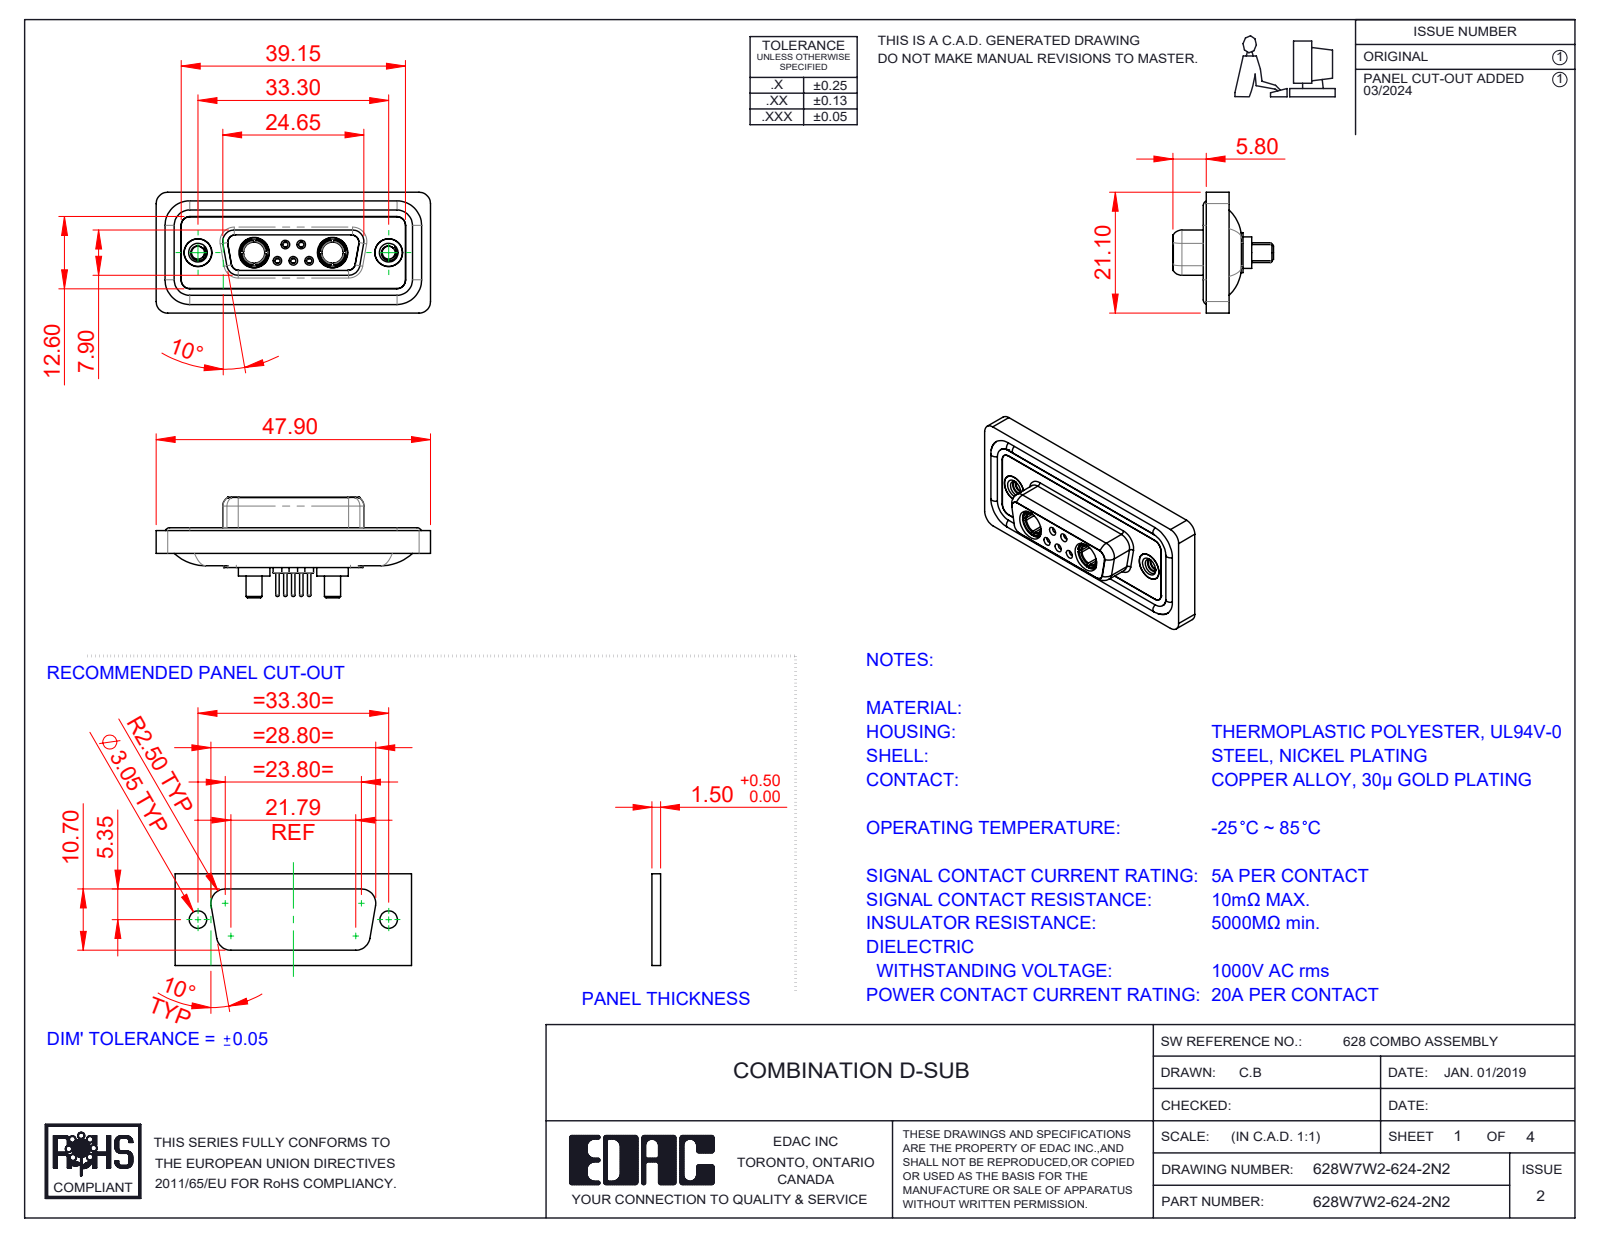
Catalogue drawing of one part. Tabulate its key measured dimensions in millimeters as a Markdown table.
| quantity | value |
| --- | --- |
| part name | 628Combo Housing_7W2; 628W7W2-624-2N2; Power Socket_20A S; 628Combo Shell Front_15 Contacts (+5 more) |
| STEP written by | SolidWorks 2023 (CONFIG_CONTROL_DESIGN) |
| units | millimeters |
| bodies | 16 solids, 809 faces (238 planar, 329 cylindrical, 242 other) |
| overall size | 47.9 × 21.1 × 17.55 |
| volume | 6 077 mm³ |
| surface area | 9 885 mm² |
| round holes (diameter × count) | 0.9 × 5, 1.1 × 5, 1.5 × 5, 2 × 5, 4.85 × 4, 1.6 × 3, 1.7 × 2, 2.26 × 2, 3.7 × 2, 4 × 2, 4.05 × 2, 5 × 2 |
| round bosses / shafts (diameter × count) | 1.6 × 6, 2.2 × 5, 0.6 × 5, 5.5 × 2, 5.2 × 2, 4.96 × 2, 4.95 × 2, 4.8 × 2 |
| partial cylindrical surfaces (radius × count) | 1.5 × 22, 2 × 20, 1.35 × 12, 1.6 × 8, 0.25 × 4, 0.5 × 4, 0.6 × 4, 0.65 × 4 |
| main face-to-face distances | 0.4, 1.8, 1.6, 0.5, 2.9, 7.45, 1.1, 5.65, 6.6, 7.05 |
| hole center spacings | 3.16, 2.77, 9.8, 23.5, 4.31, 4.33, 5.03, 5.04 |
